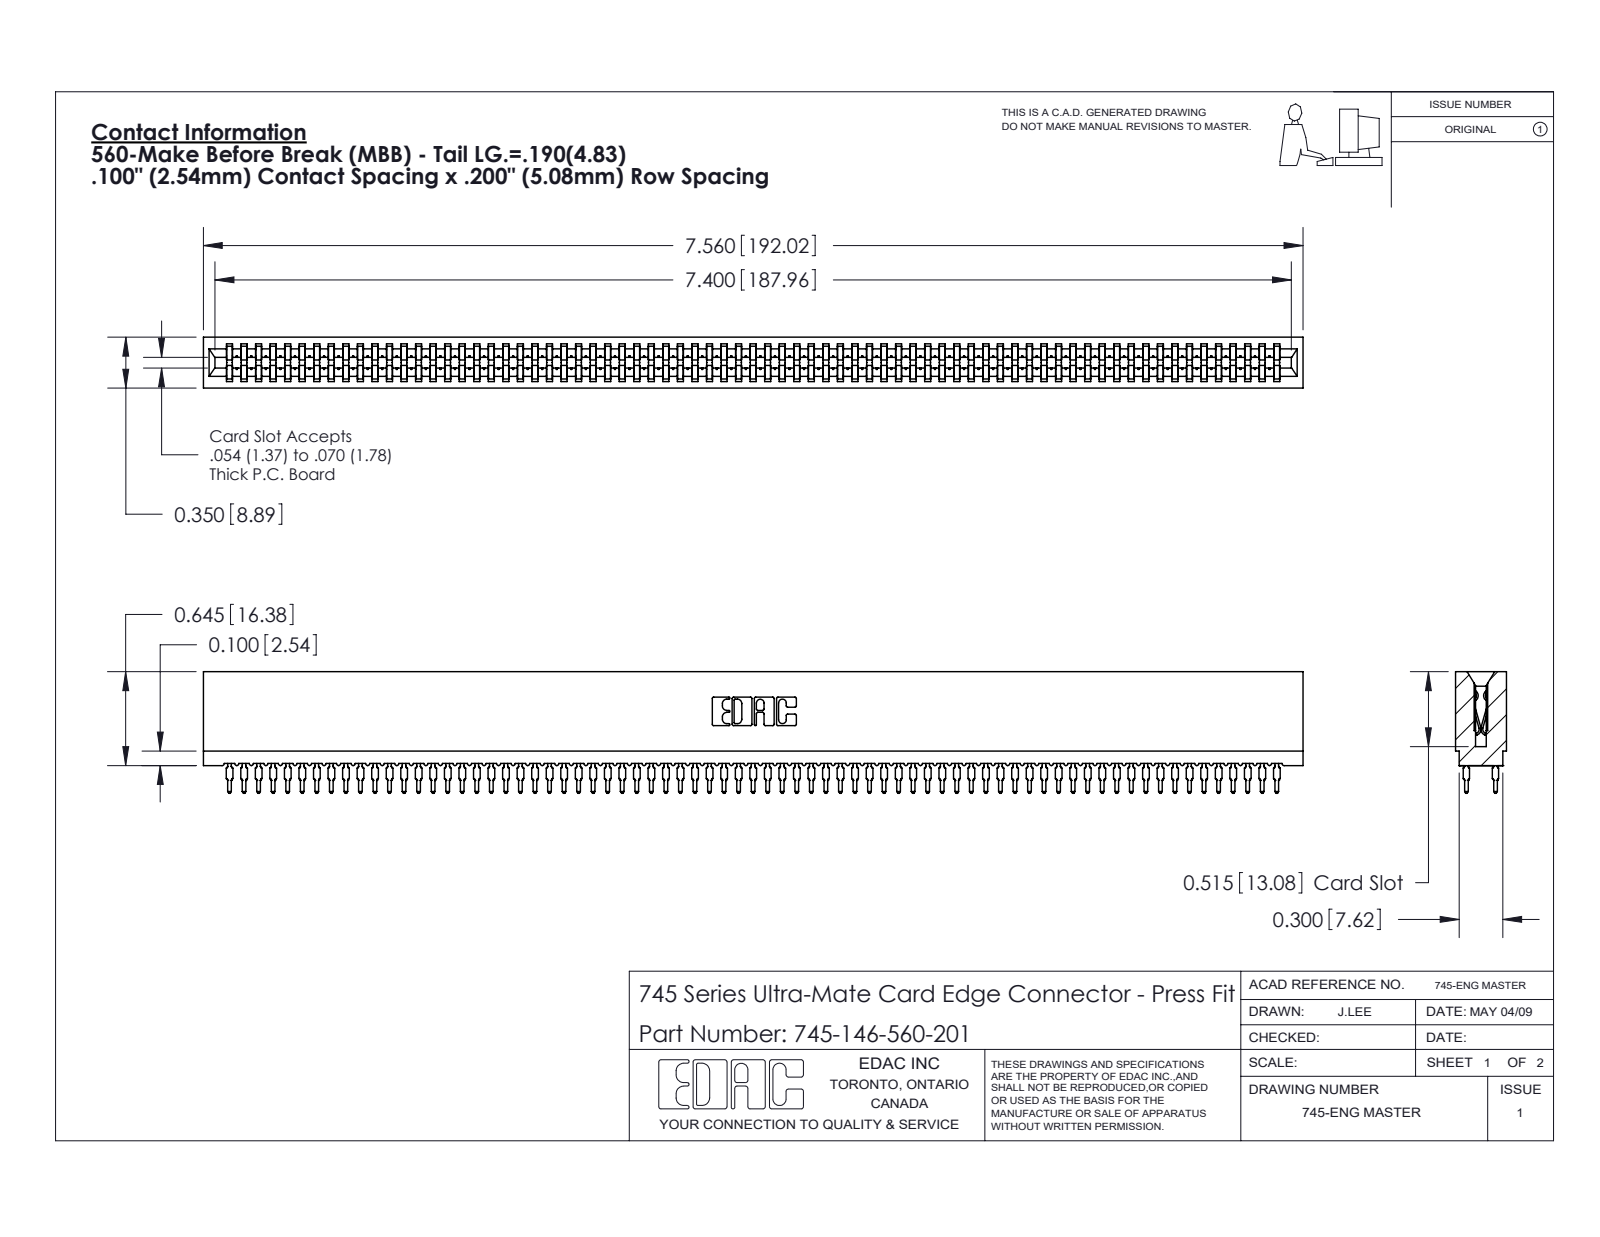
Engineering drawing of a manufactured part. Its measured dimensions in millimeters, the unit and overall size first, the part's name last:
Units: millimetres
Overall size (bounding box): 192 × 21.2 × 8.9
Partial cylindrical surfaces — rounded edges, fillets, slot ends (radius × count): R0.5 ×292, R0.4 ×146, R0.3 ×22, R0.1 ×8, R0.3 ×8, R0.2 ×6, R0.8 ×6, R0.7 ×3
Main face-to-face distances: 8.9, 1.6, 7.3, 1.1, 7.7, 0.5, 6.2, 3.5, 5.4, 2.4
Volume: 17 650 mm³ · Surface area: 38 900 mm²
Bodies: 147 solids, 14476 faces (7501 planar, 3179 cylindrical, 3796 other)
Part name (STEP PRODUCT): 745-292-001_560; 745 Part_Insulator Option - 01; 745-146-560-201
STEP written by: SolidWorks 2020 (CONFIG_CONTROL_DESIGN)
